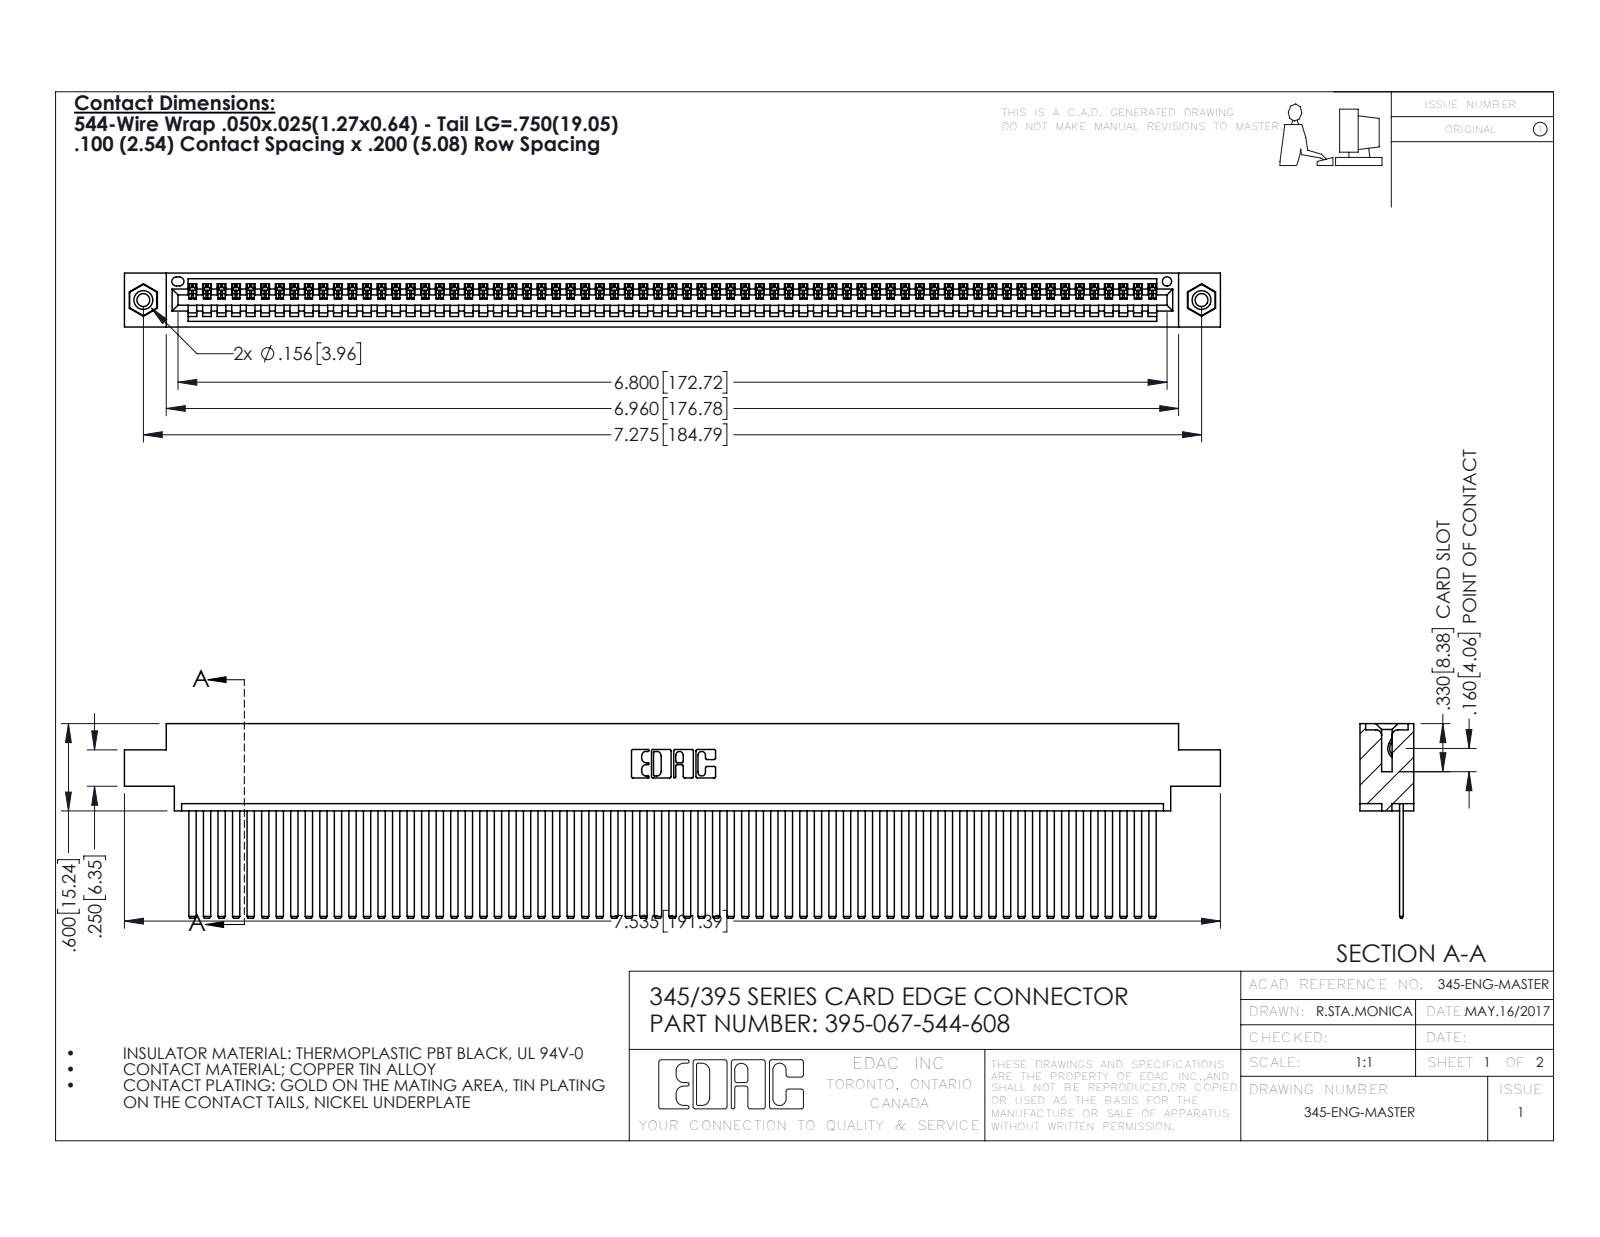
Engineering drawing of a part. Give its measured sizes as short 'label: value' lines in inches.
name: 345-292-001_345-293-144; 345 Part_0.170 Offset - 0.156 Dia-TI; 395-067-544-608; 345-250-001_345-250-003-102
written by: SolidWorks 2016 (CONFIG_CONTROL_DESIGN)
unit: in
bodies: 70 solids, 3674 faces (2528 planar, 1130 cylindrical, 16 other)
size: 7.535 × 1.337 × 0.37
volume: 1.162 in³; area: 43.58 in²
holes: 2× ⌀0.089, 2× ⌀0.125, 2× ⌀0.156, 1× ⌀0.064
bosses: 2× ⌀0.155
rounds: 134× R0.006, 22× R0.01, 6× R0.007, 6× R0.031, 3× R0.026, 2× R0.031, 2× R0.04, 1× R0.014
face distances: 0.072, 0.298, 0.025, 0.098, 0.272, 0.37, 0.2, 0.225, 0.175, 0.149
hole spacings: 0.27, 7.039, 7.275
